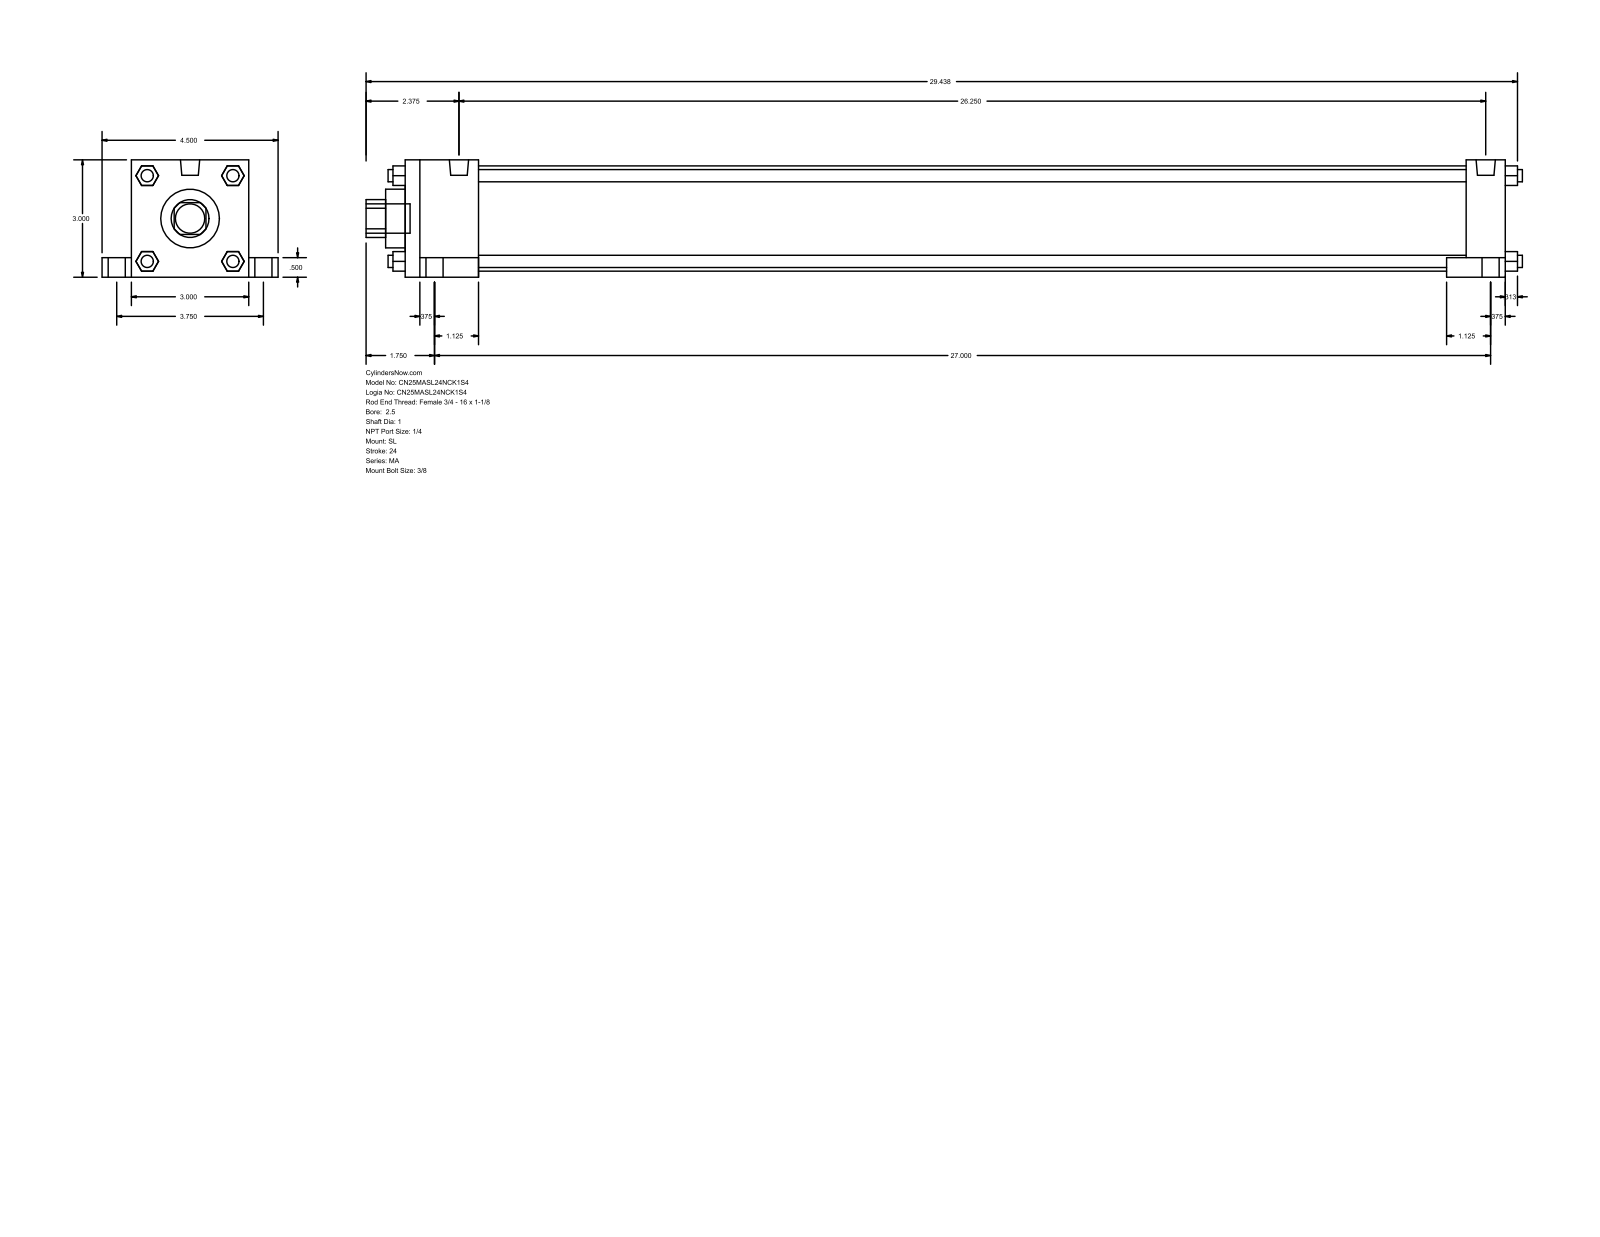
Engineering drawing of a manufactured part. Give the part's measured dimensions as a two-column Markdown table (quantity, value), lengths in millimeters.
| quantity | value |
| --- | --- |
| part name | MA_SL__0250_1 |
| STEP written by | GSSL Pune (CONFIG_CONTROL_DESIGN) |
| units | millimeters |
| bodies | 0 solids, 148 faces (112 planar, 36 cylindrical, 0 other) |
| overall size | 750.89 × 114.3 × 76.2 |
| round holes (diameter × count) | 25.4 × 1, 38.1 × 1, 68.33 × 1 |
| round bosses / shafts (diameter × count) | 7.94 × 8, 17.46 × 4, 11.11 × 4, 12.49 × 2, 19.05 × 1 |
| partial cylindrical surfaces (radius × count) | 12.29 × 1 |
| main face-to-face distances | 76.2, 714.37, 12.7, 641.35, 25.39, 47.63, 666.74, 688.98, 19.05, 95.25 |
